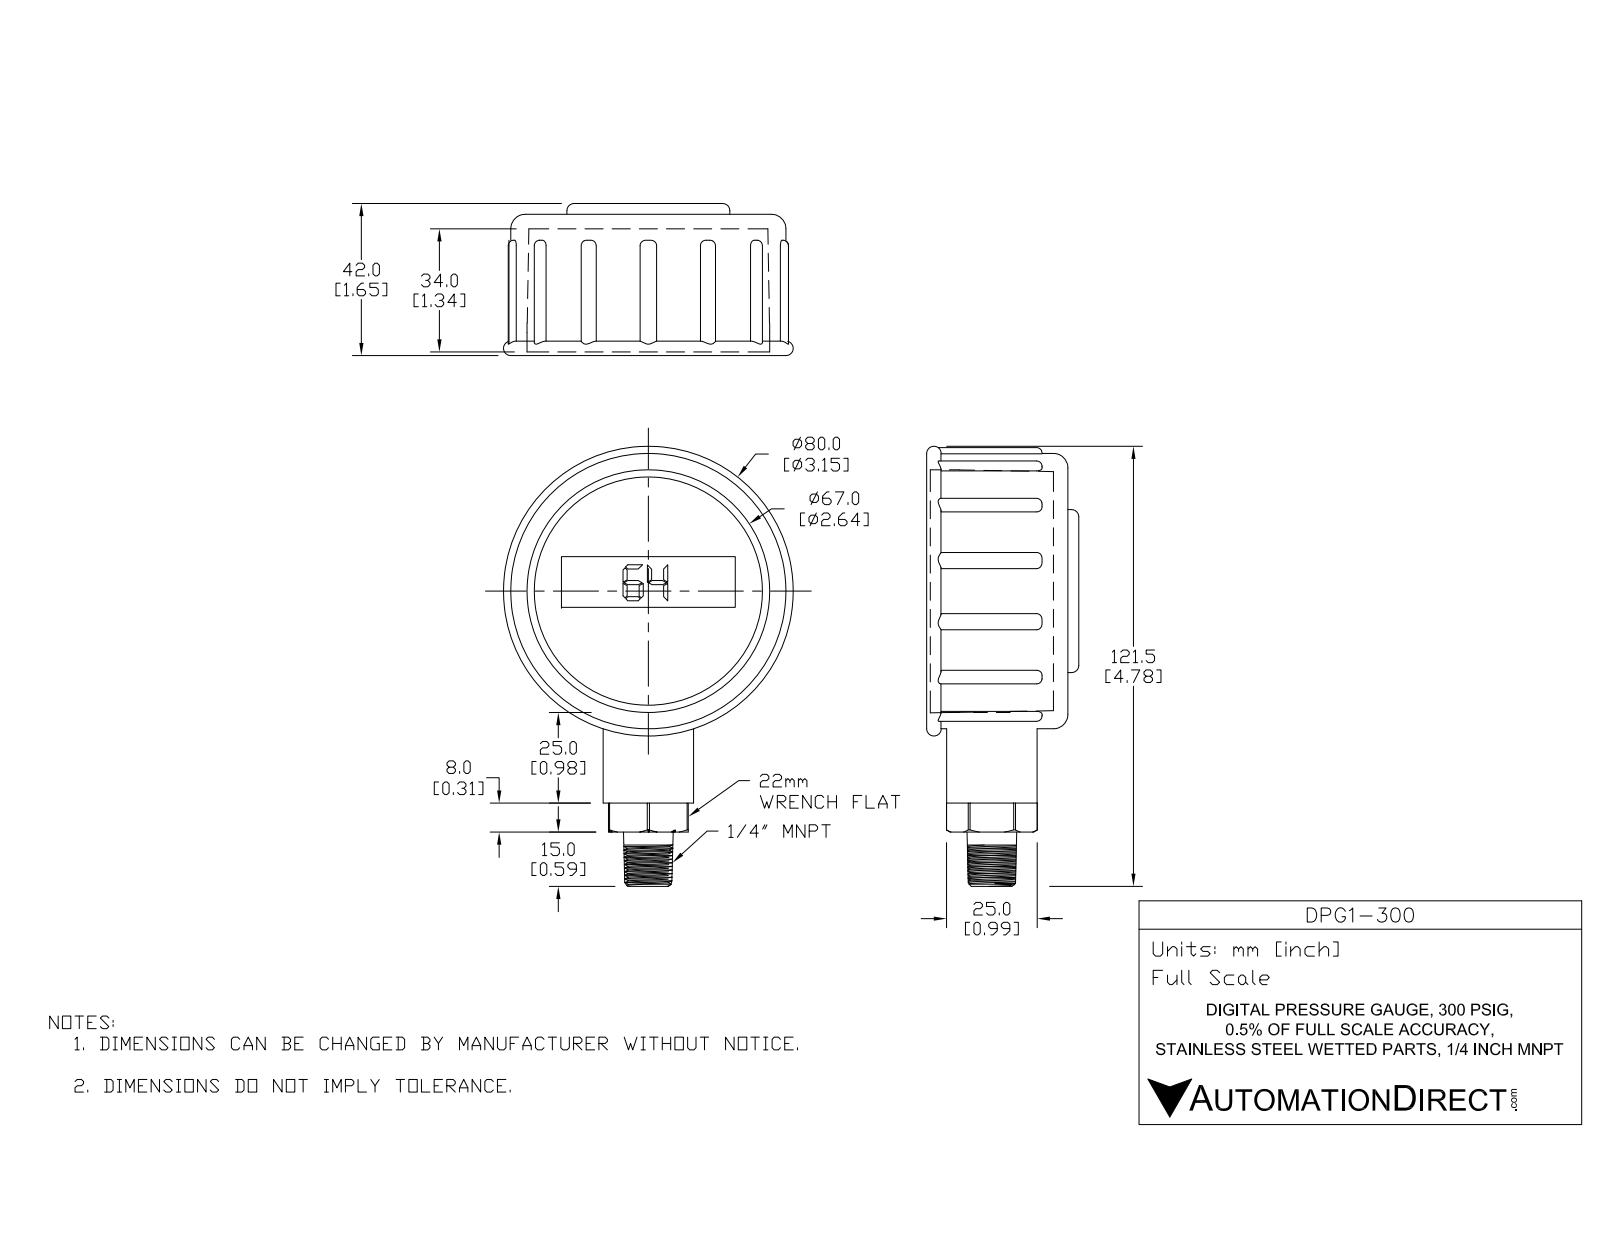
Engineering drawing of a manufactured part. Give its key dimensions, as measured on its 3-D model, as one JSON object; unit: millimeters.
{"part_name": "DPG1-300", "step_written_by": "SolidWorks 2021 (CONFIG_CONTROL_DESIGN)", "units": "millimeters", "bodies": {"solids": 4, "faces": 181, "planar": 71, "cylindrical": 49, "other": 61}, "overall_size": [121.62, 80, 42], "volume_mm3": 196180, "surface_area_mm2": 45978, "round_holes": [[63, 1], [67.19, 1]], "round_bosses_or_shafts": [[76, 1], [67, 1], [45, 1], [25, 1], [10, 1]], "partial_cylinders_radius": [[2.38, 13], [8.5, 6], [38, 1]], "face_to_face_distances": [33.95, 4, 37.95, 3, 7, 40.95, 42, 39, 35, 1.05]}
